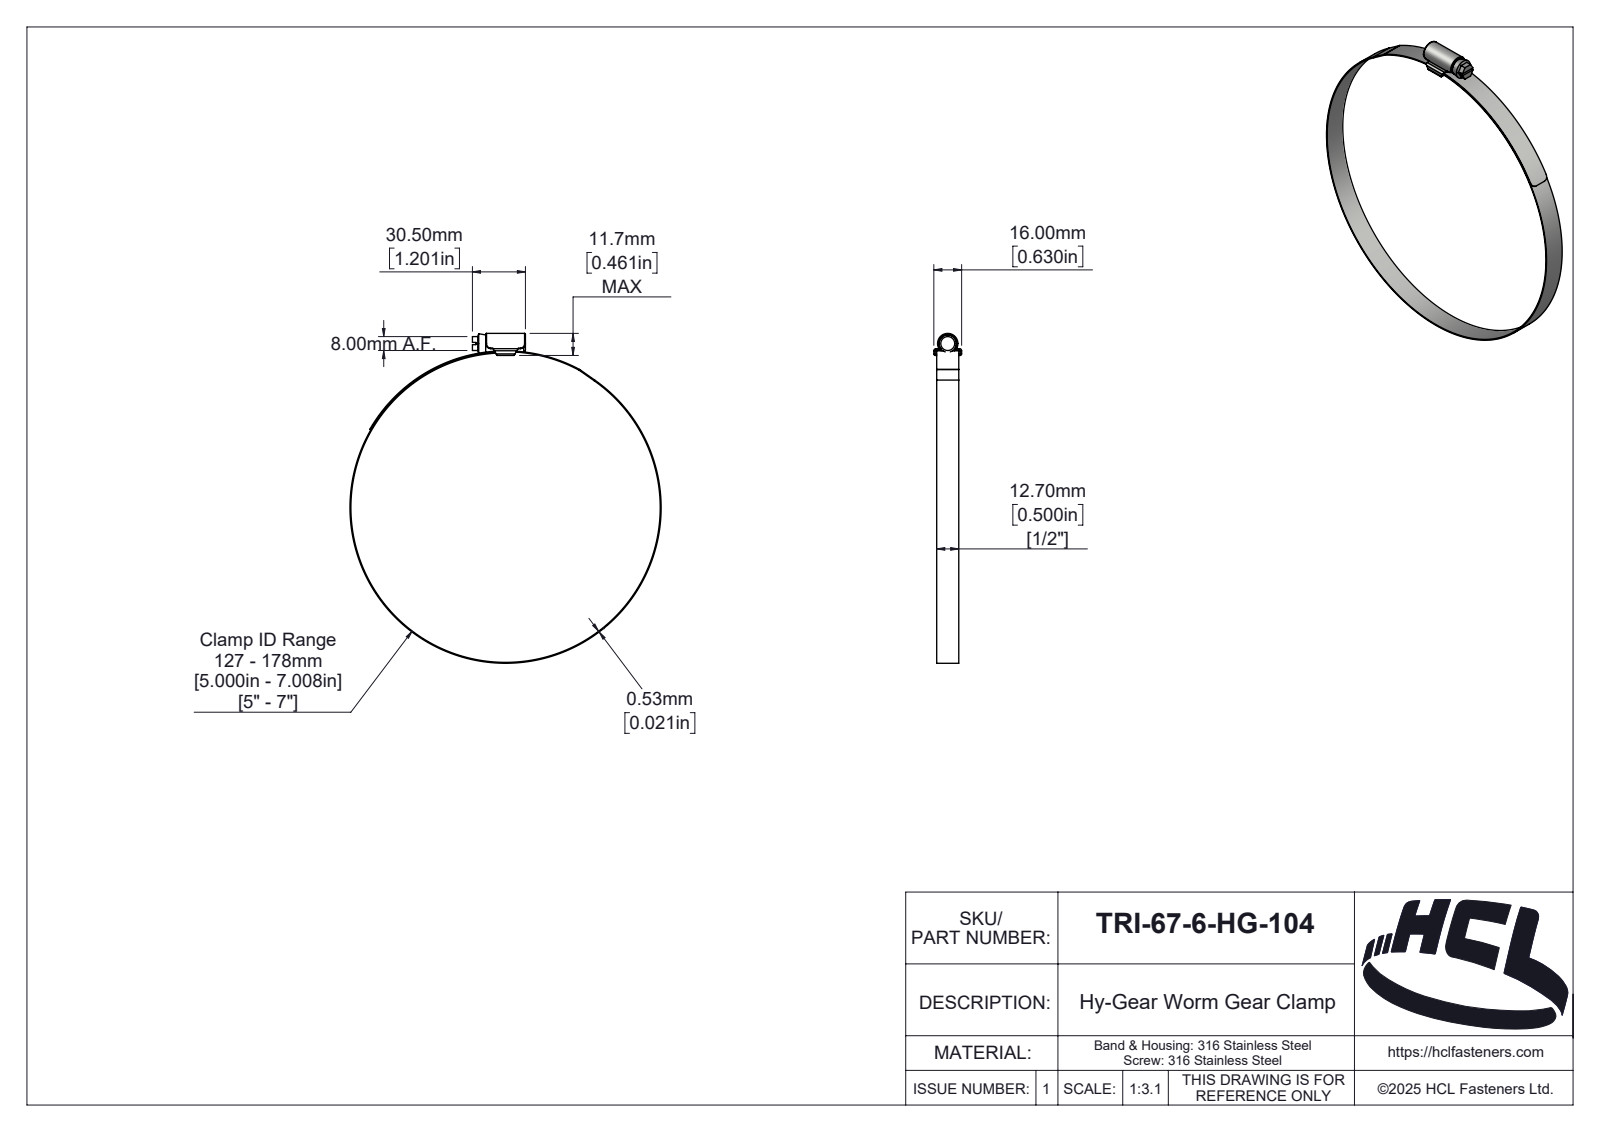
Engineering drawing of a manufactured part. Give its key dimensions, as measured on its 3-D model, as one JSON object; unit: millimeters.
{"part_name": "TRI-57-0-HG-104", "step_written_by": "SolidWorks 2025 (AUTOMOTIVE_DESIGN)", "units": "millimeters", "bodies": {"solids": 3, "faces": 189, "planar": 39, "cylindrical": 89, "other": 61}, "overall_size": [189.73, 179.06, 16], "volume_mm3": 7402, "surface_area_mm2": 20245, "round_holes": [[178, 1]], "round_bosses_or_shafts": [[179.06, 1], [10, 1]], "partial_cylinders_radius": [[0.5, 6], [3, 4], [0.1, 2], [0.9, 2], [1.2, 2], [0.46, 1], [1.89, 1], [2, 1]], "face_to_face_distances": [12.7, 0.8, 0.53, 3.1, 2.3, 3.9, 30.5, 1.65, 14.35, 15.2]}
